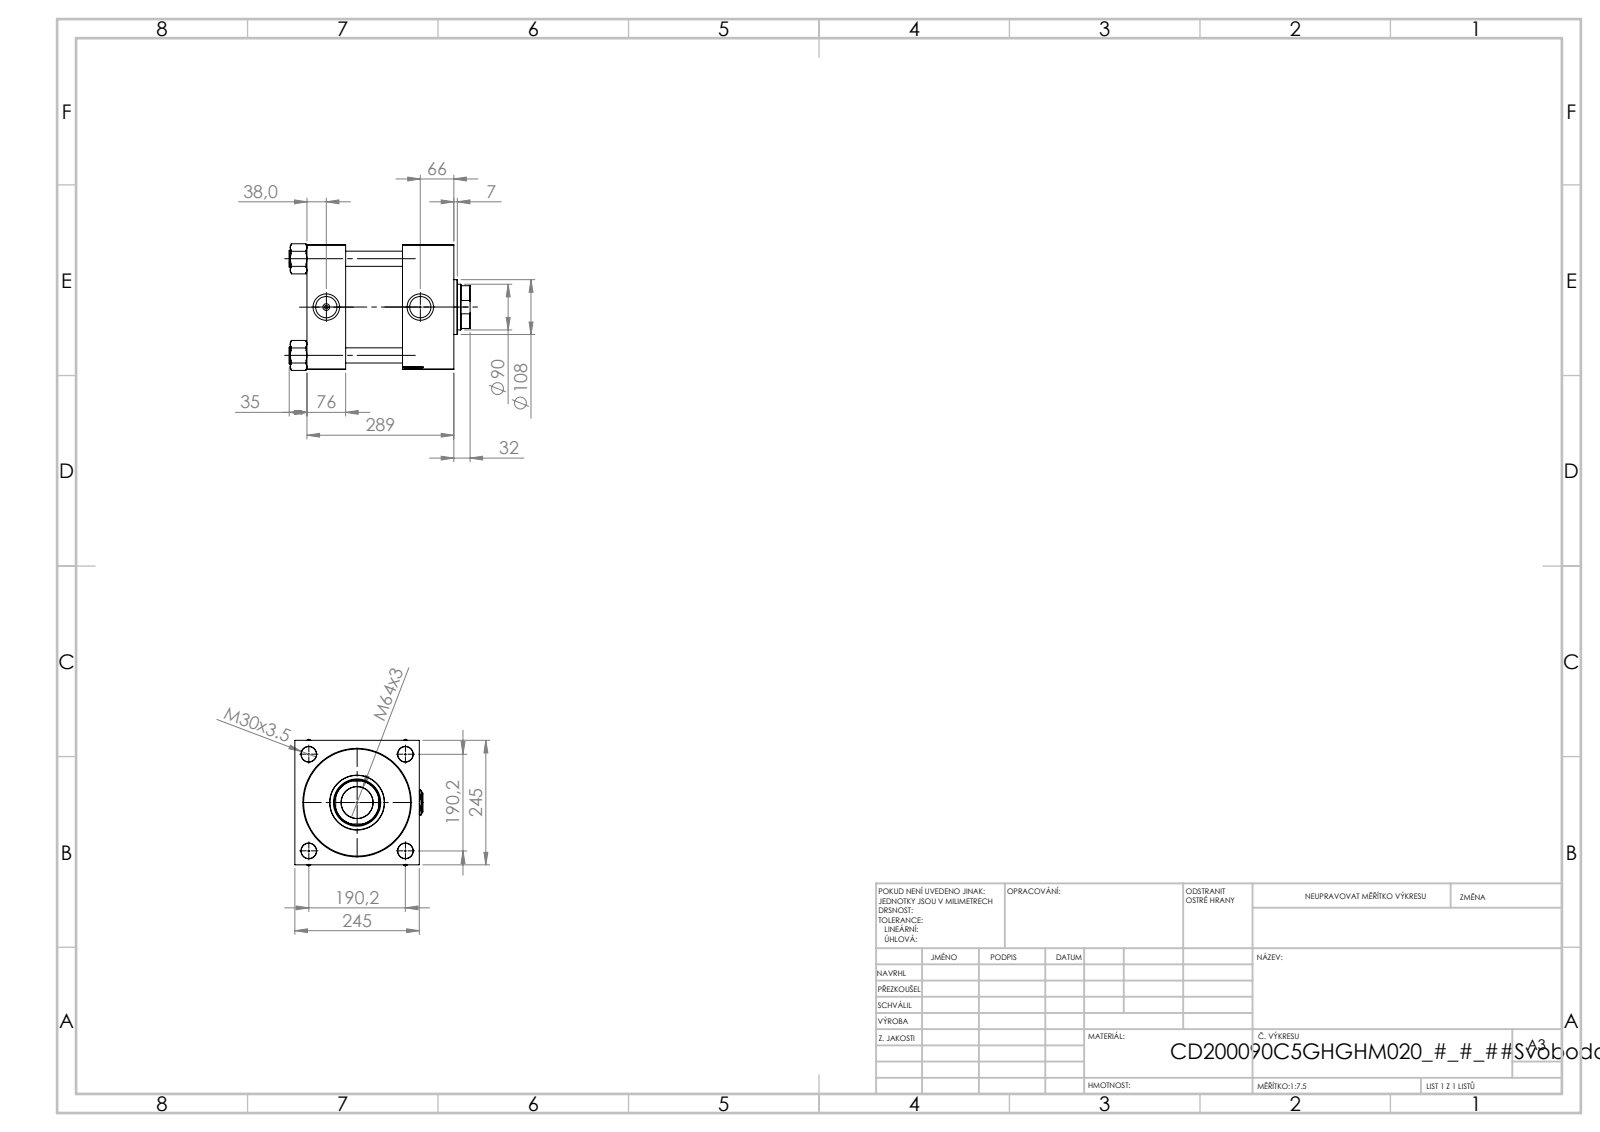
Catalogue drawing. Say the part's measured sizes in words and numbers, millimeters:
The part is named "NUT_M5_V215CD_C; V215CD_Body_C; V215CD_VC_C; V215CD_VCP_C (+2 more)". Its 3-D file was written by "SolidWorks 2019 (CONFIG_CONTROL_DESIGN)". It is 12 solids with 1250 faces: 598 planar, 94 cylindrical and 558 other. Overall it measures 356 by 252 by 249.44 millimeters. Its volume is 13 430 000 cubic millimeters and its surface area 1 047 000 square millimeters. Round holes: 4 of diameter 30, 2 of diameter 7, 2 of diameter 41.92, 2 of diameter 52, 1 of diameter 62.5, 1 of diameter 90, 1 of diameter 93, 1 of diameter 146, 1 of diameter 200, 1 of diameter 210.5. Round bosses or shafts: 4 of diameter 33, 1 of diameter 206, 1 of diameter 108. Partial cylindrical surfaces (rounded edges, fillets, slot ends): 1 of radius 44. The main face-to-face distances are 245, 76, 289, 213, 260.3, 184.3, 28.7, 188, 112, 72.3. The hole center spacings are 134.49, 190.2, 268.98, 185.
